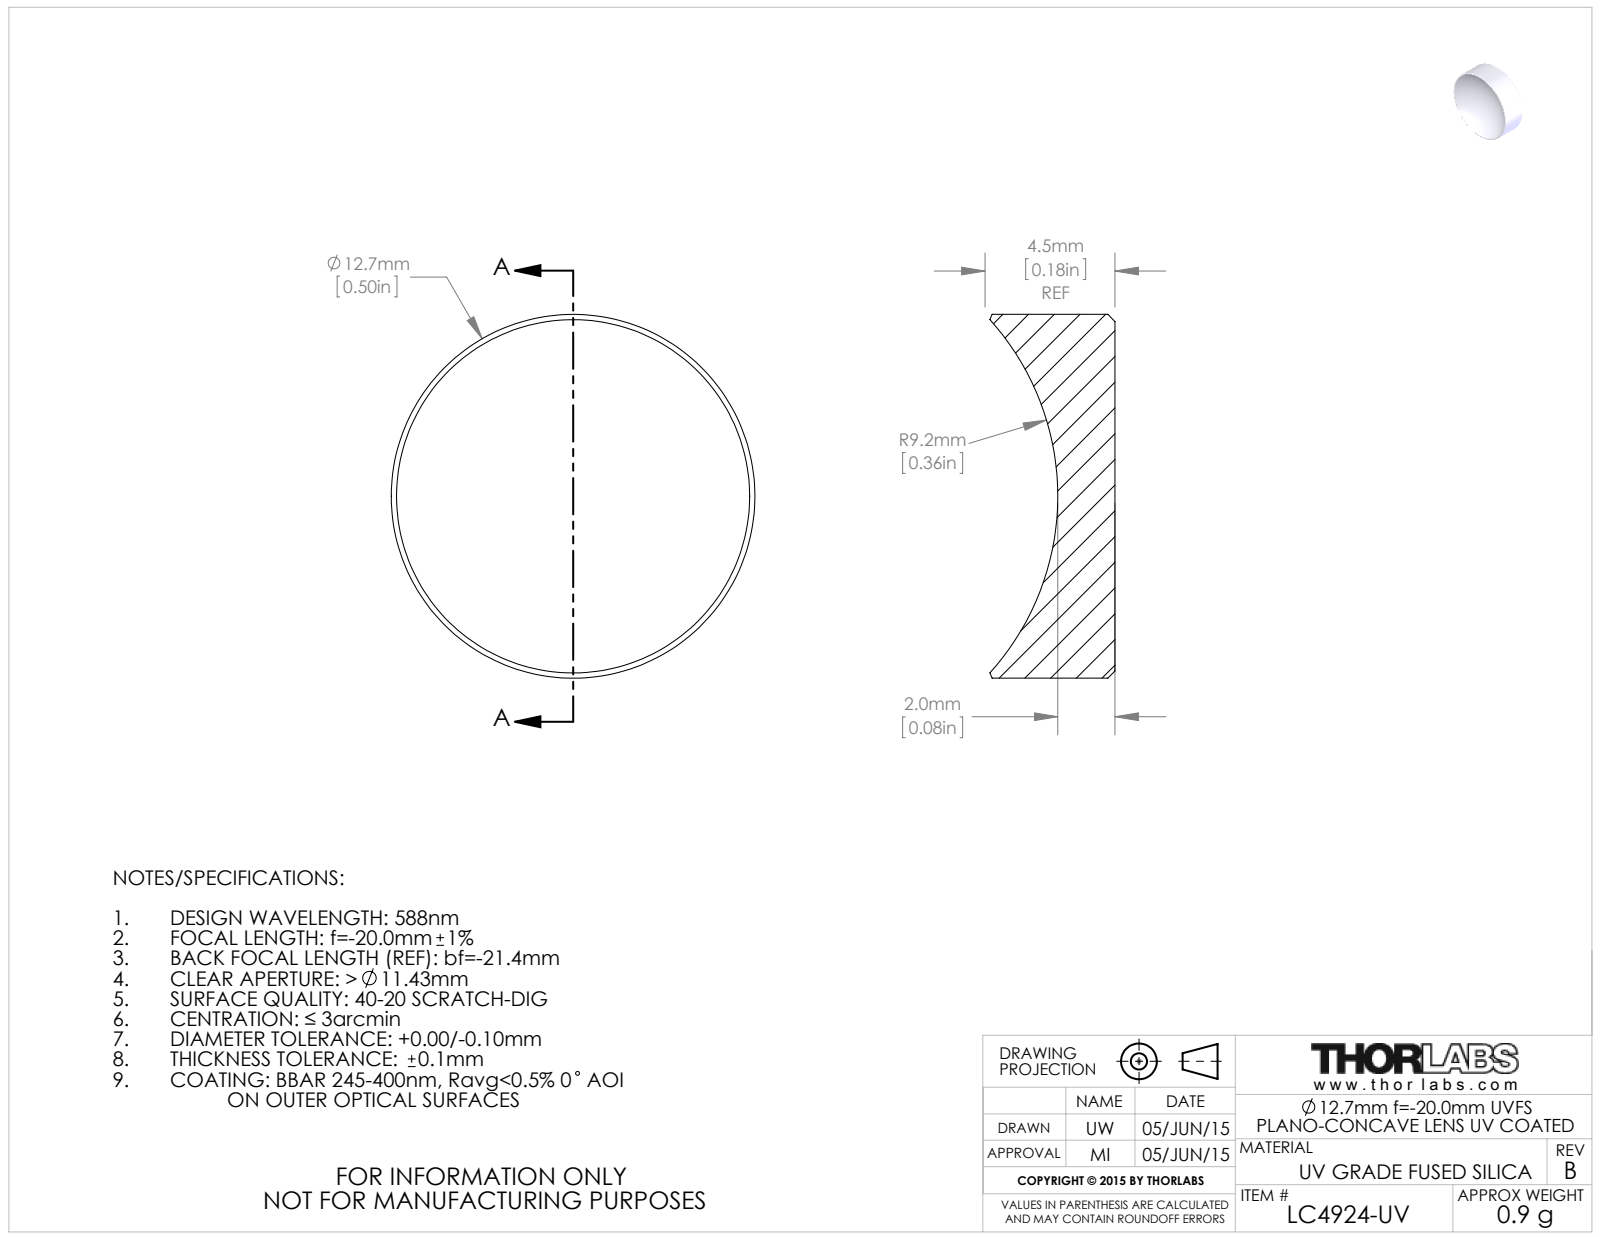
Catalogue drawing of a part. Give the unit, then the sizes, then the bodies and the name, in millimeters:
Units: millimetres
Overall size (bounding box): 12.7 × 12.7 × 4.37
Round bosses / shafts (diameter × count): ⌀12.7 ×1
Volume: 404 mm³ · Surface area: 437 mm²
Bodies: 1 solid, 9 faces (1 planar, 2 cylindrical, 6 other)
Part name (STEP PRODUCT): 4343-E0W
STEP written by: SolidWorks 2014 (CONFIG_CONTROL_DESIGN)
